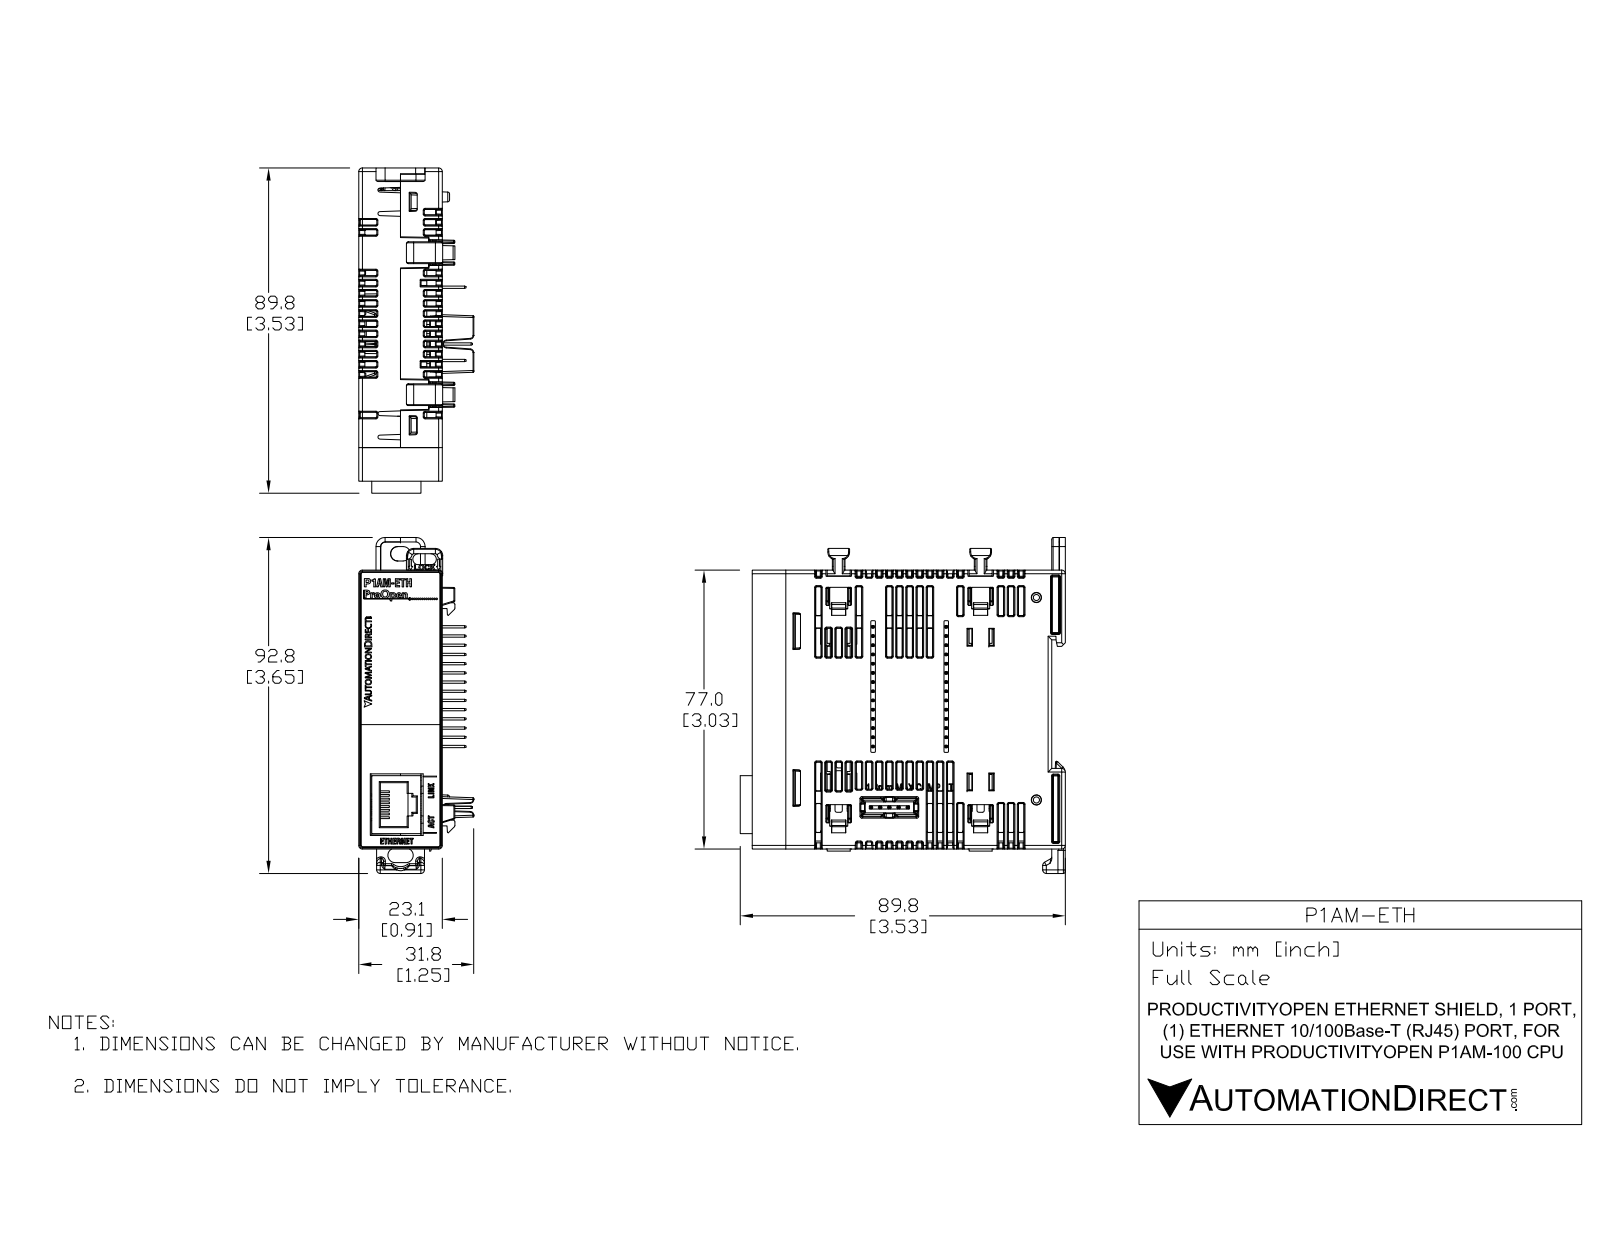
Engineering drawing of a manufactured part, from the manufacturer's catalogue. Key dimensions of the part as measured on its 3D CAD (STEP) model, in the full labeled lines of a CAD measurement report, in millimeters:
Part name (STEP PRODUCT): P1AM-ETH EXT w sketches 3Cr1 comb1 from 2XT 1B2r1 C1r1
STEP written by: SolidWorks 2017 (AUTOMOTIVE_DESIGN)
Units: millimetres
Bodies: 25 solids, 3058 faces (2052 planar, 443 cylindrical, 563 other)
Overall size (bounding box): 92.8 × 89.8 × 31.8
Volume: 141 700 mm³ · Surface area: 35 150 mm²
Round holes (diameter × count): ⌀0.3 ×33, ⌀3.1 ×2
Round bosses / shafts (diameter × count): ⌀2 ×2
Partial cylindrical surfaces — rounded edges, fillets, slot ends (radius × count): R0.5 ×125, R0.3 ×95, R1 ×30, R1 ×23, R2 ×11, R0.4 ×4, R1.2 ×4, R1.2 ×4
Main face-to-face distances: 23, 77, 8.9, 9.2, 21.4, 1.7, 73.4, 82.3, 82.6, 1.7
Hole centre spacings: 2.5, 20.4, 5.1, 20.8, 7.6, 21.6, 10.2, 22.6
